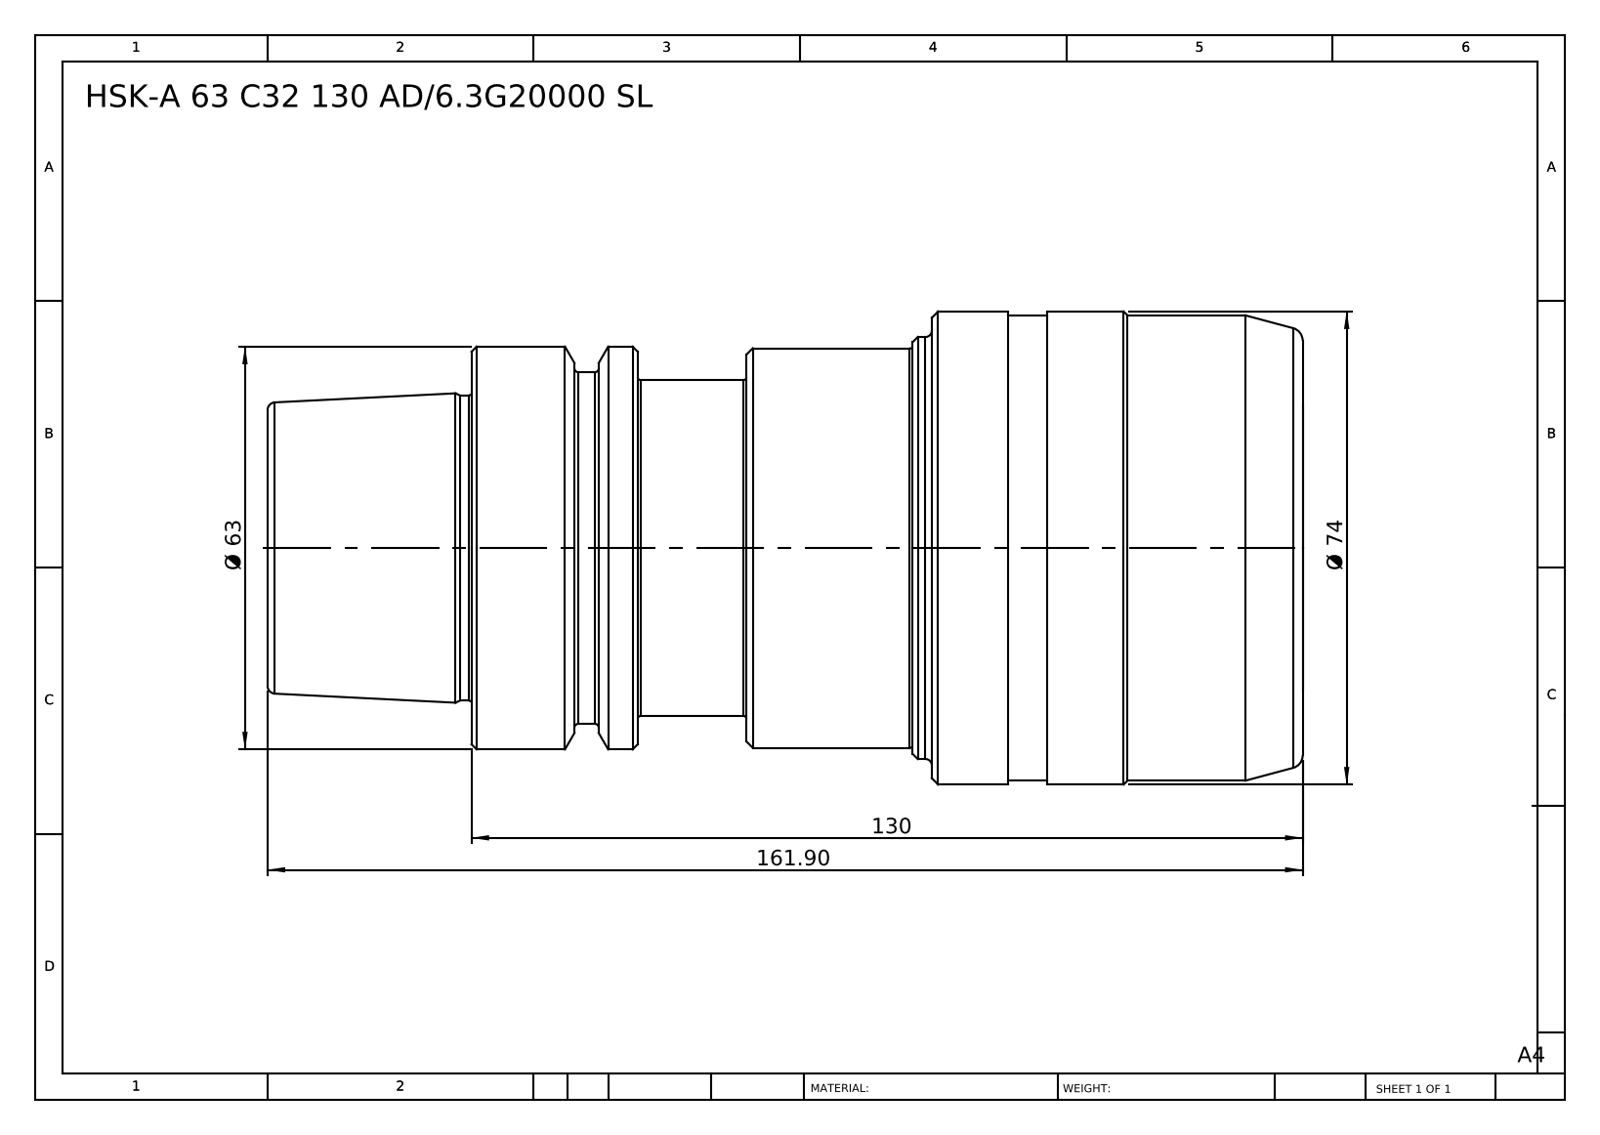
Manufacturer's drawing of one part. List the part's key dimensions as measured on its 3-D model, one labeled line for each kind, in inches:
Part name (STEP PRODUCT): HSK-A C32 130 AD-6.3G20000 SL
STEP written by: SolidWorks 2014 (CONFIG_CONTROL_DESIGN)
Units: inches
Bodies: 1 solid, 78 faces (12 planar, 22 cylindrical, 44 other)
Overall size (bounding box): 6.374 × 2.913 × 2.913
Volume: 30.61 in³ · Surface area: 64.77 in²
Round bosses / shafts (diameter × count): ⌀2.913 ×1, ⌀2.866 ×1, ⌀2.598 ×1, ⌀2.48 ×1, ⌀2.461 ×1, ⌀2.165 ×1, ⌀2.067 ×1, ⌀1.881 ×1
Main face-to-face distances: 6.374, 1.024, 5.118, 1.256, 1.693, 4.094, 2.28, 3.425, 0.669, 2.949
